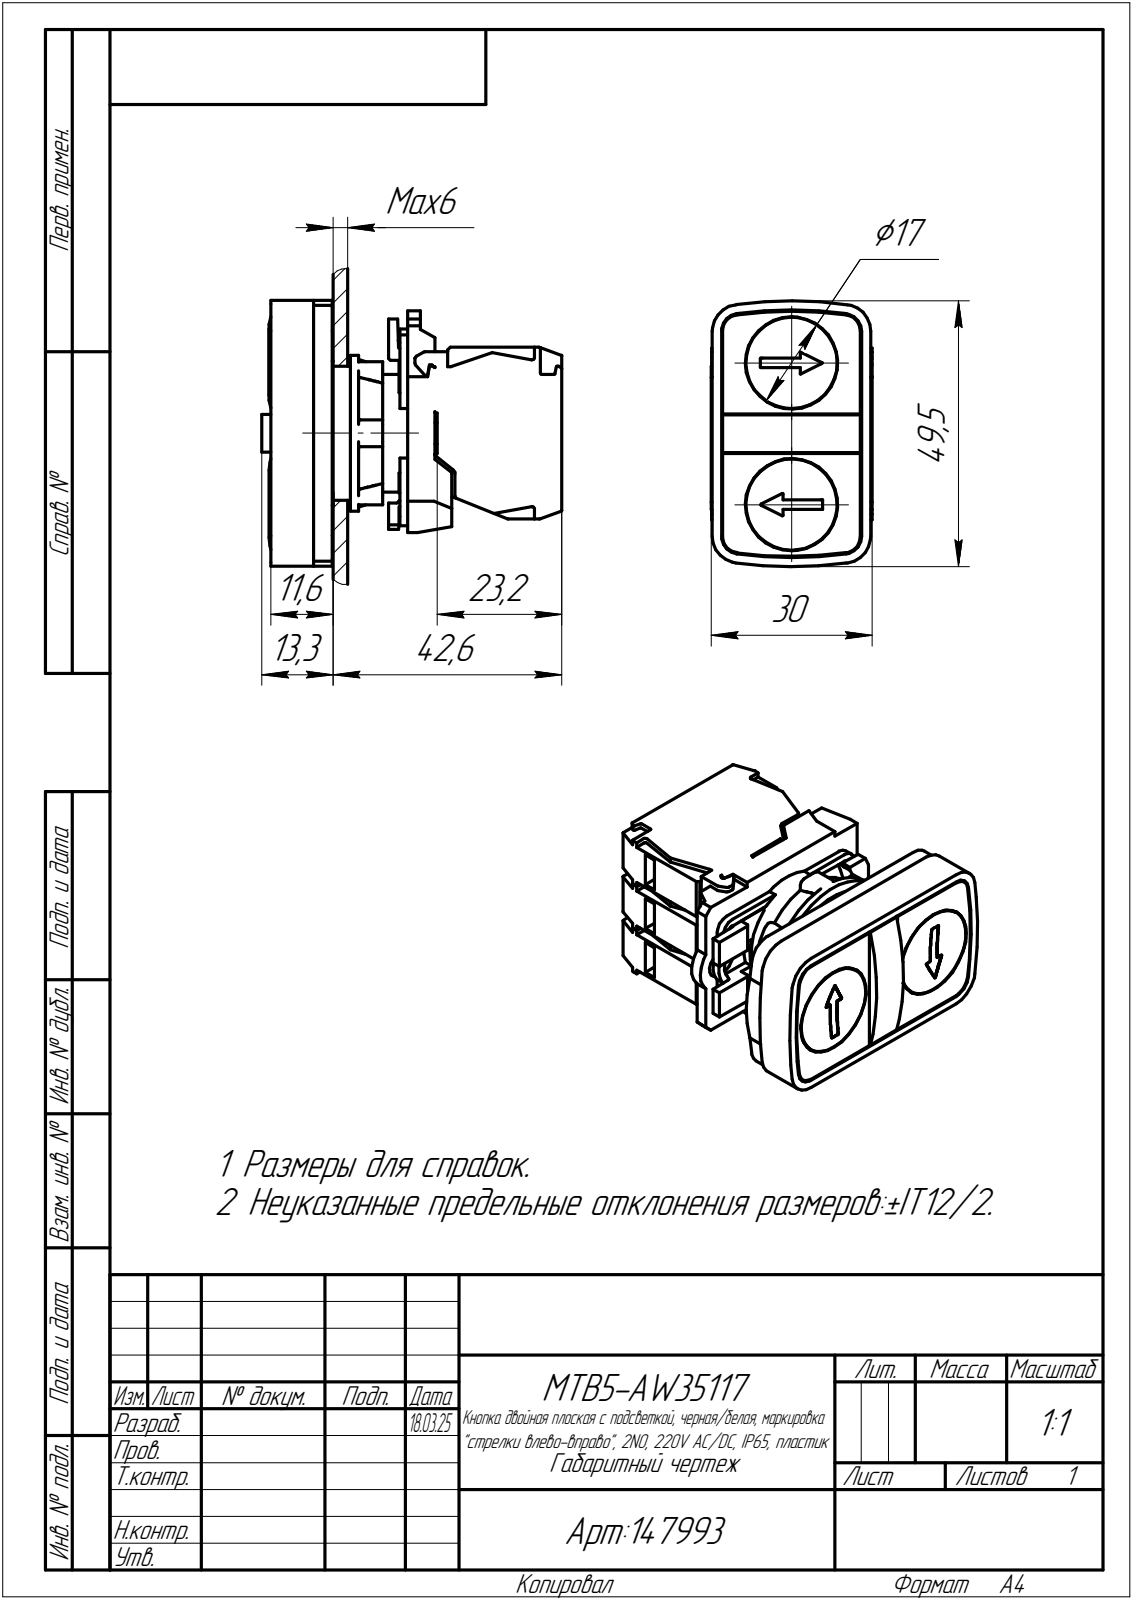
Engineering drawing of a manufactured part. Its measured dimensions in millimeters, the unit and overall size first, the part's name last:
Units: millimetres
Overall size (bounding box): 55.9 × 49.5 × 30
Round holes (diameter × count): ⌀6 ×2, ⌀17.2 ×2, ⌀5.2 ×1, ⌀20.5 ×1
Round bosses / shafts (diameter × count): ⌀17 ×2, ⌀29 ×1, ⌀26.8 ×1, ⌀25 ×1, ⌀22 ×1
Partial cylindrical surfaces — rounded edges, fillets, slot ends (radius × count): R1 ×15, R0.2 ×13, R0.1 ×10, R0.5 ×7, R2.5 ×4, R3.1 ×4, R3.3 ×4, R4.35 ×4
Main face-to-face distances: 10, 9.9, 20, 19.9, 10.1, 14.1, 9, 25.5, 11.4, 19.1
Hole centre spacings: 4.7, 8.5, 13.2, 21.7, 17, 26.4
Volume: 47 702 mm³ · Surface area: 19 407 mm²
Bodies: 1 solid, 659 faces (451 planar, 187 cylindrical, 21 other)
Part name (STEP PRODUCT): MTB5-AW35117
STEP written by: C3D Toolkit (CONFIG_CONTROL_DESIGN)
